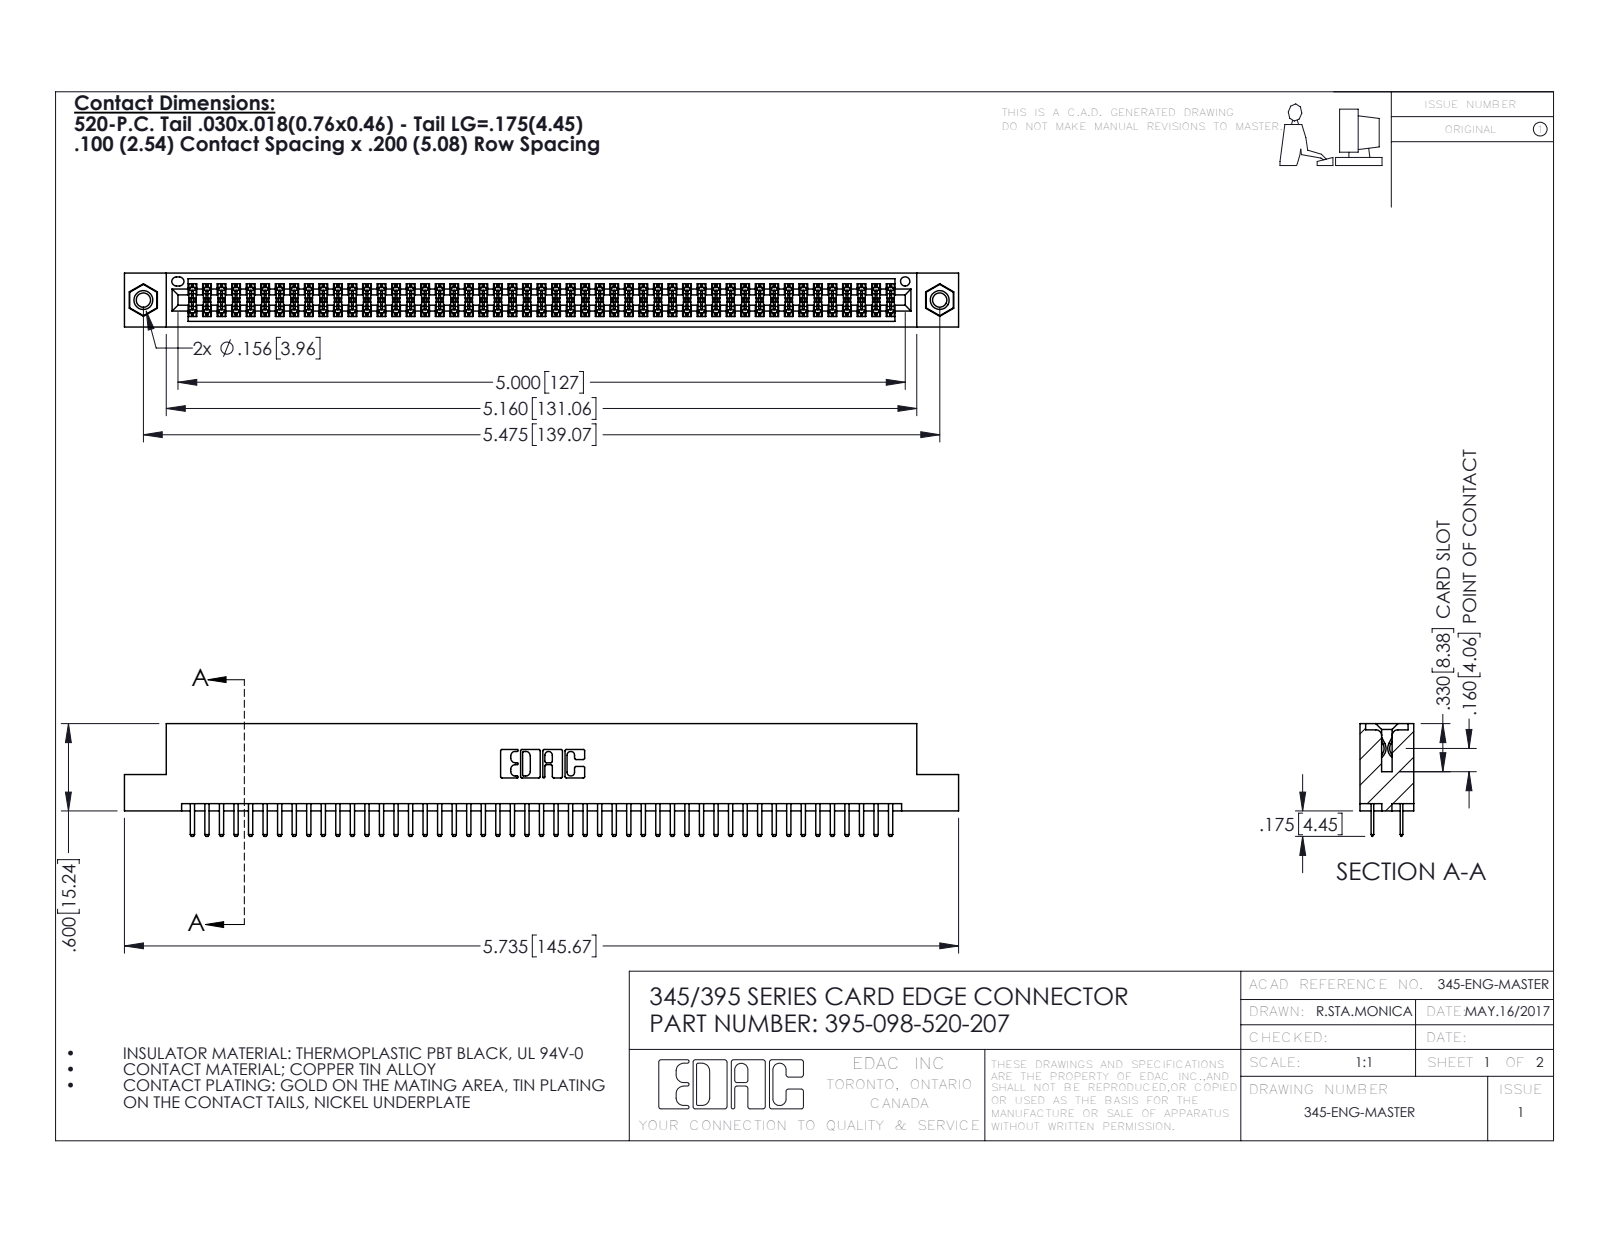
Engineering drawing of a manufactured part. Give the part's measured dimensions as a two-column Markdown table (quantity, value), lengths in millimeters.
| quantity | value |
| --- | --- |
| part name | 395-098-520-207; 345-250-001_345-250-005-103; 345 Part_Flush Mounting Lugs - 0.156 Dia-TI; 345-292-001_345-293-120 |
| STEP written by | SolidWorks 2016 (CONFIG_CONTROL_DESIGN) |
| units | millimeters |
| bodies | 101 solids, 5478 faces (3542 planar, 1920 cylindrical, 16 other) |
| overall size | 145.7 × 19.7 × 9.4 |
| volume | 14 200 mm³ |
| surface area | 21 000 mm² |
| round holes (diameter × count) | 2.5 × 2, 3.2 × 2, 4 × 2, 1.6 × 1 |
| round bosses / shafts (diameter × count) | 3.9 × 2 |
| partial cylindrical surfaces (radius × count) | 0.2 × 147, 0.3 × 102, 0.3 × 22, 0.2 × 6, 0.8 × 6, 0.7 × 3, 0.4 × 2, 0.5 × 2 |
| main face-to-face distances | 1.8, 7.6, 5.1, 9.4, 2.5, 6.9, 0.6, 5.7, 0.6, 1.8 |
| hole center spacings | 6.9, 133.1, 139.1 |
